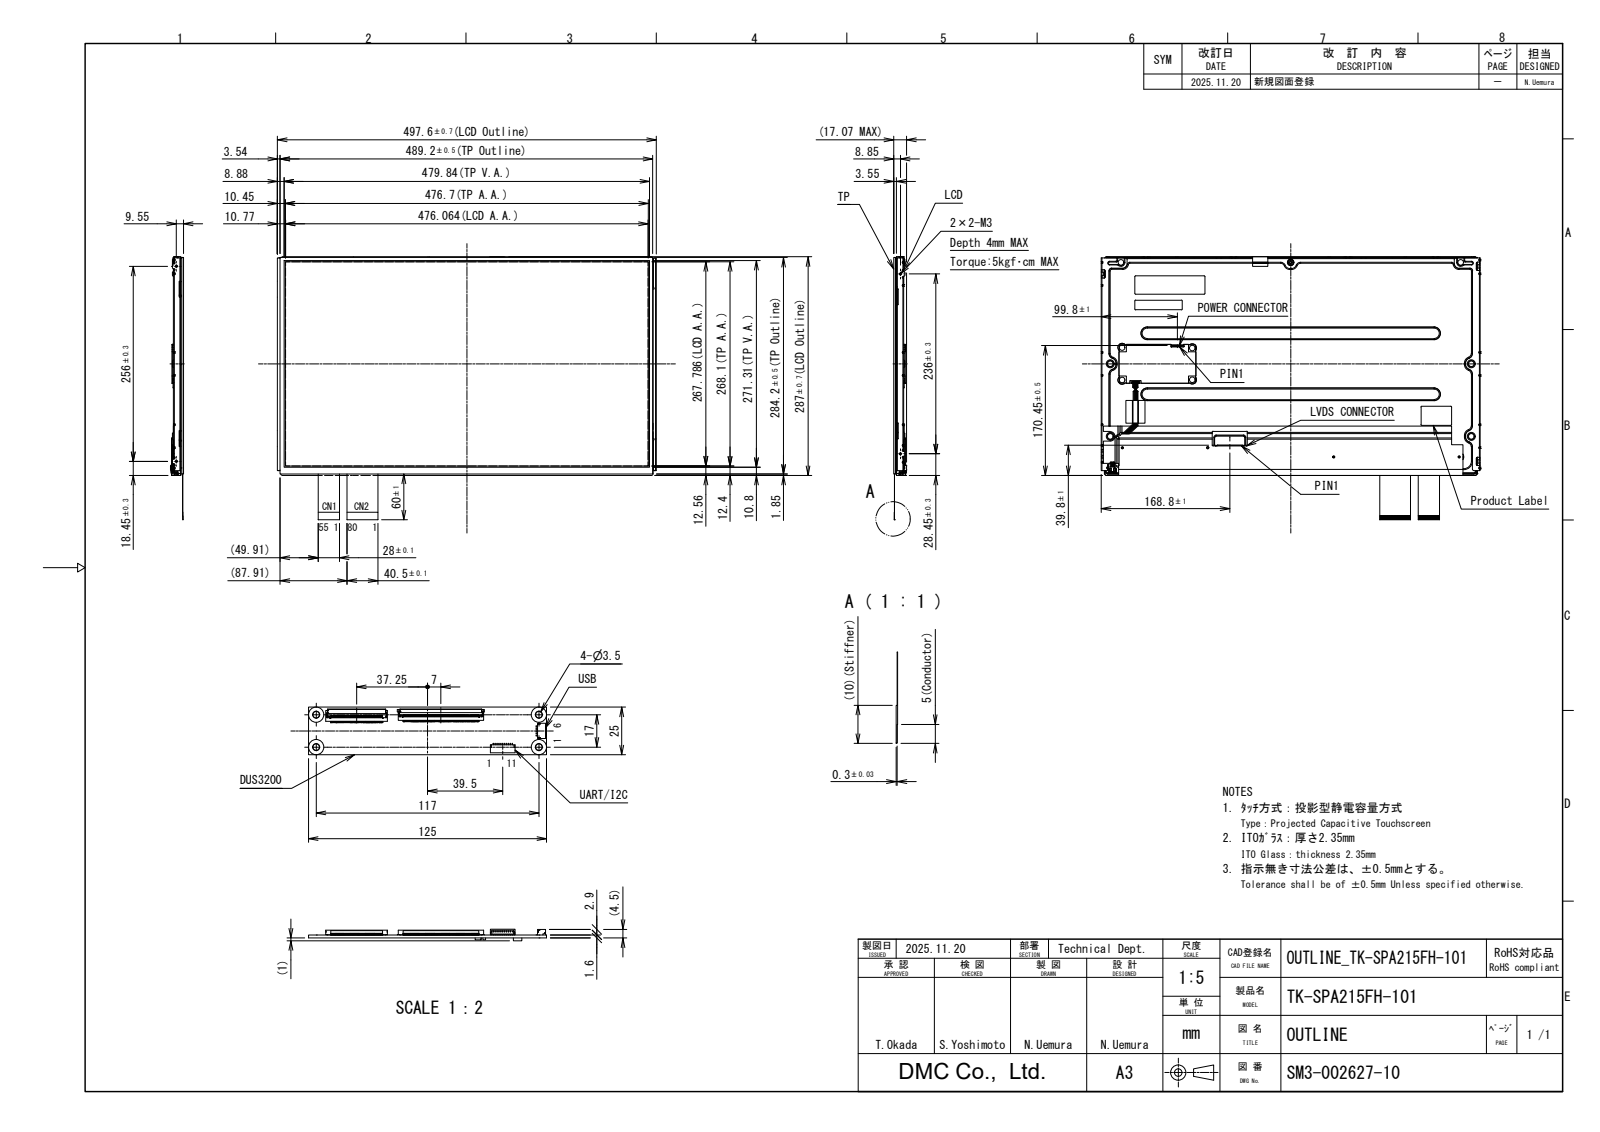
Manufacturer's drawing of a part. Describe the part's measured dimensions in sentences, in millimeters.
The part is named "TK-SPA215FH-101". Its 3-D file was written by "Autodesk Inventor 2024 (AUTOMOTIVE_DESIGN)". It is 1 solid with 12262 faces: 7878 planar, 3470 cylindrical and 914 other. Overall it measures 497.6 by 345.15 by 17.07 millimeters. Its volume is 807 166 cubic millimeters and its surface area 795 673 square millimeters. Round holes: 10 of diameter 3, 4 of diameter 4, 4 of diameter 6.5, 2 of diameter 0.9, 2 of diameter 1.1, 2 of diameter 2.3, 2 of diameter 3.6, 2 of diameter 6, 2 of diameter 8, 1 of diameter 2. Round bosses or shafts: 47 of diameter 0.87, 7 of diameter 4.6, 6 of diameter 7.5, 6 of diameter 3, 6 of diameter 2.5, 4 of diameter 7, 4 of diameter 4.5, 4 of diameter 4. Partial cylindrical surfaces (rounded edges, fillets, slot ends): 641 of radius 0.1, 397 of radius 0.2, 238 of radius 1, 215 of radius 0.5, 158 of radius 0.3, 127 of radius 0.15, 110 of radius 0.7, 49 of radius 0.9. The main face-to-face distances are 0.8, 4.61, 6.54, 11.15, 5.74, 10.35, 0.5, 1.3, 1.8, 0.6. The hole center spacings are 5.9, 10.02, 92, 101.13, 106.12, 112.02, 165.81, 223.
